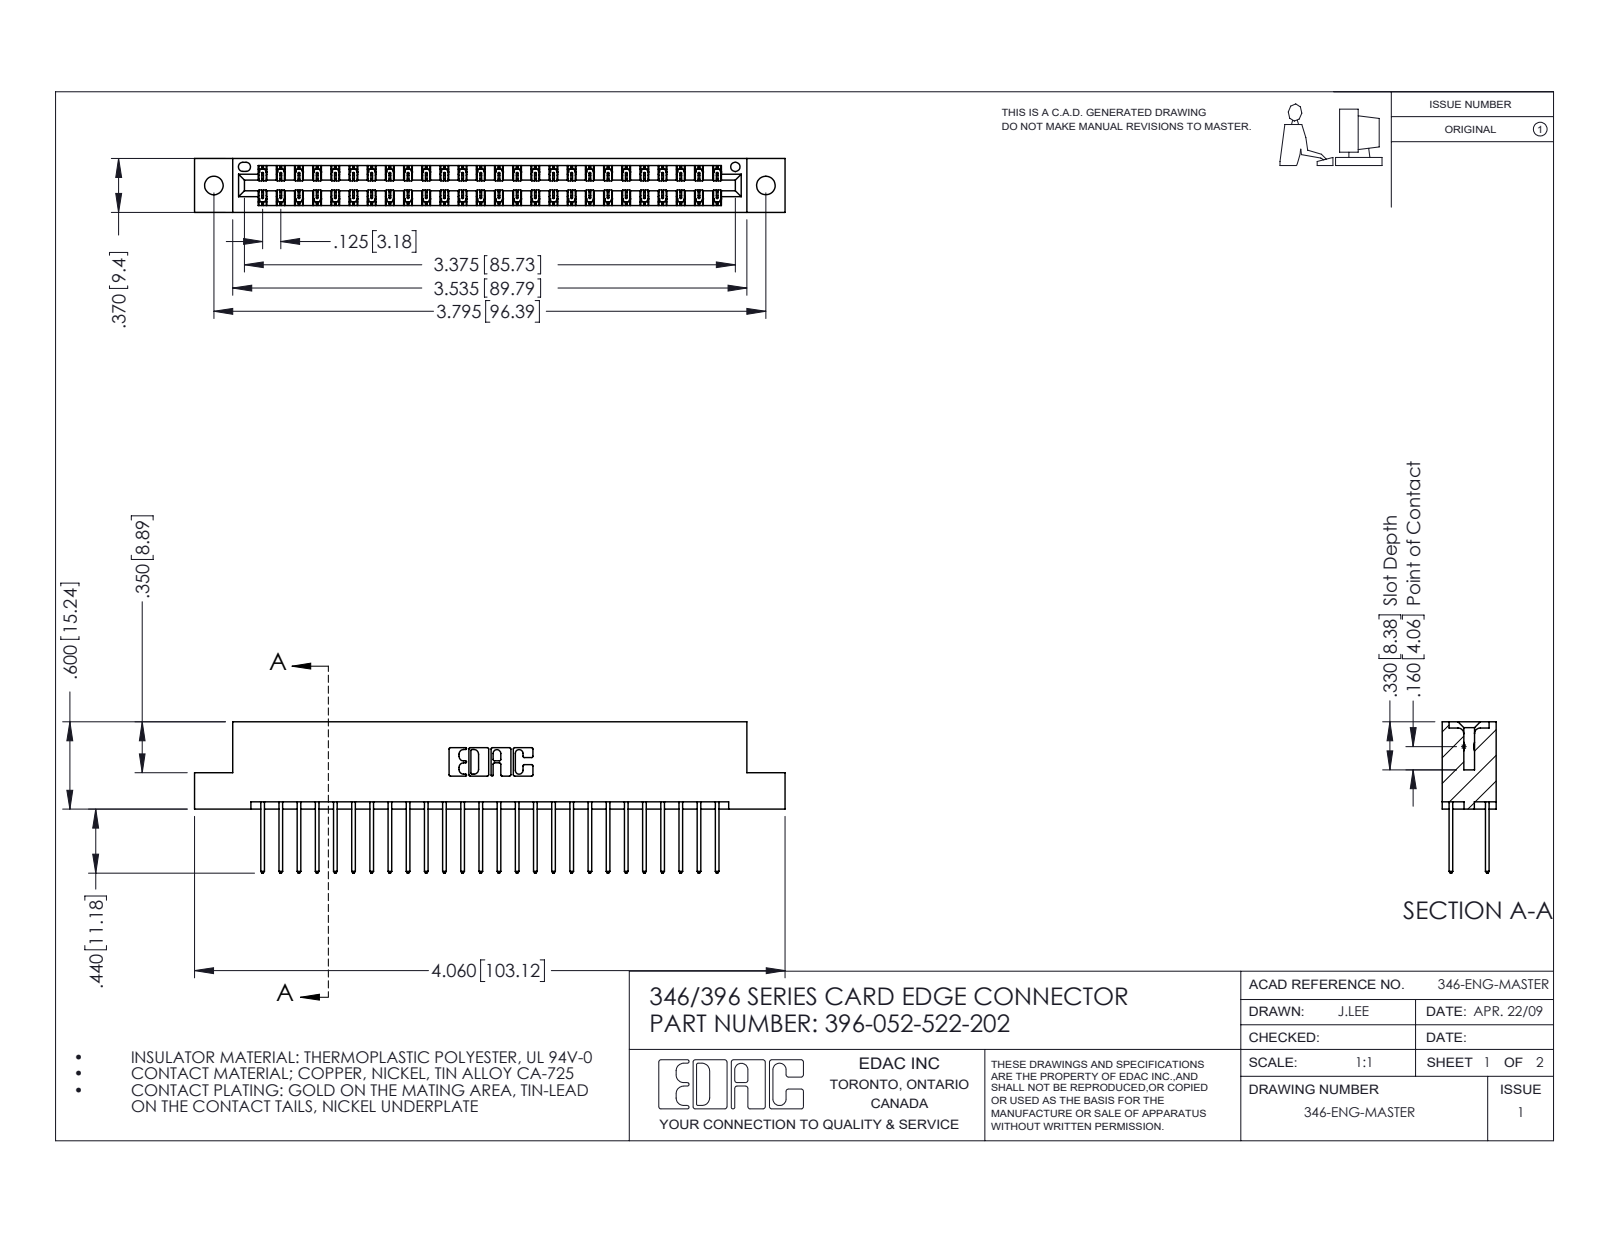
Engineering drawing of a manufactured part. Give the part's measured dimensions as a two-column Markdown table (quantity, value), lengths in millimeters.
| quantity | value |
| --- | --- |
| part name | 346 Part_Flush Mounting Lugs - 0.128 Dia; 396-052-522-202; 345-292-001_345-293-122 |
| STEP written by | SolidWorks 2016 (CONFIG_CONTROL_DESIGN) |
| units | millimeters |
| bodies | 53 solids, 2826 faces (1896 planar, 930 cylindrical, 0 other) |
| overall size | 103.1 × 26.4 × 9.4 |
| volume | 10 000 mm³ |
| surface area | 13 880 mm² |
| round holes (diameter × count) | 3.3 × 2, 1.6 × 1 |
| partial cylindrical surfaces (radius × count) | 0.2 × 78, 0.3 × 52, 0.3 × 22, 0.2 × 6, 0.8 × 6, 0.7 × 3, 0.4 × 2, 0.6 × 2 |
| main face-to-face distances | 1.2, 8.2, 6.4, 9.4, 1.8, 7.6, 0.6, 7, 3.8, 5.6 |
| hole center spacings | 6.2, 91.1, 96.4 |
